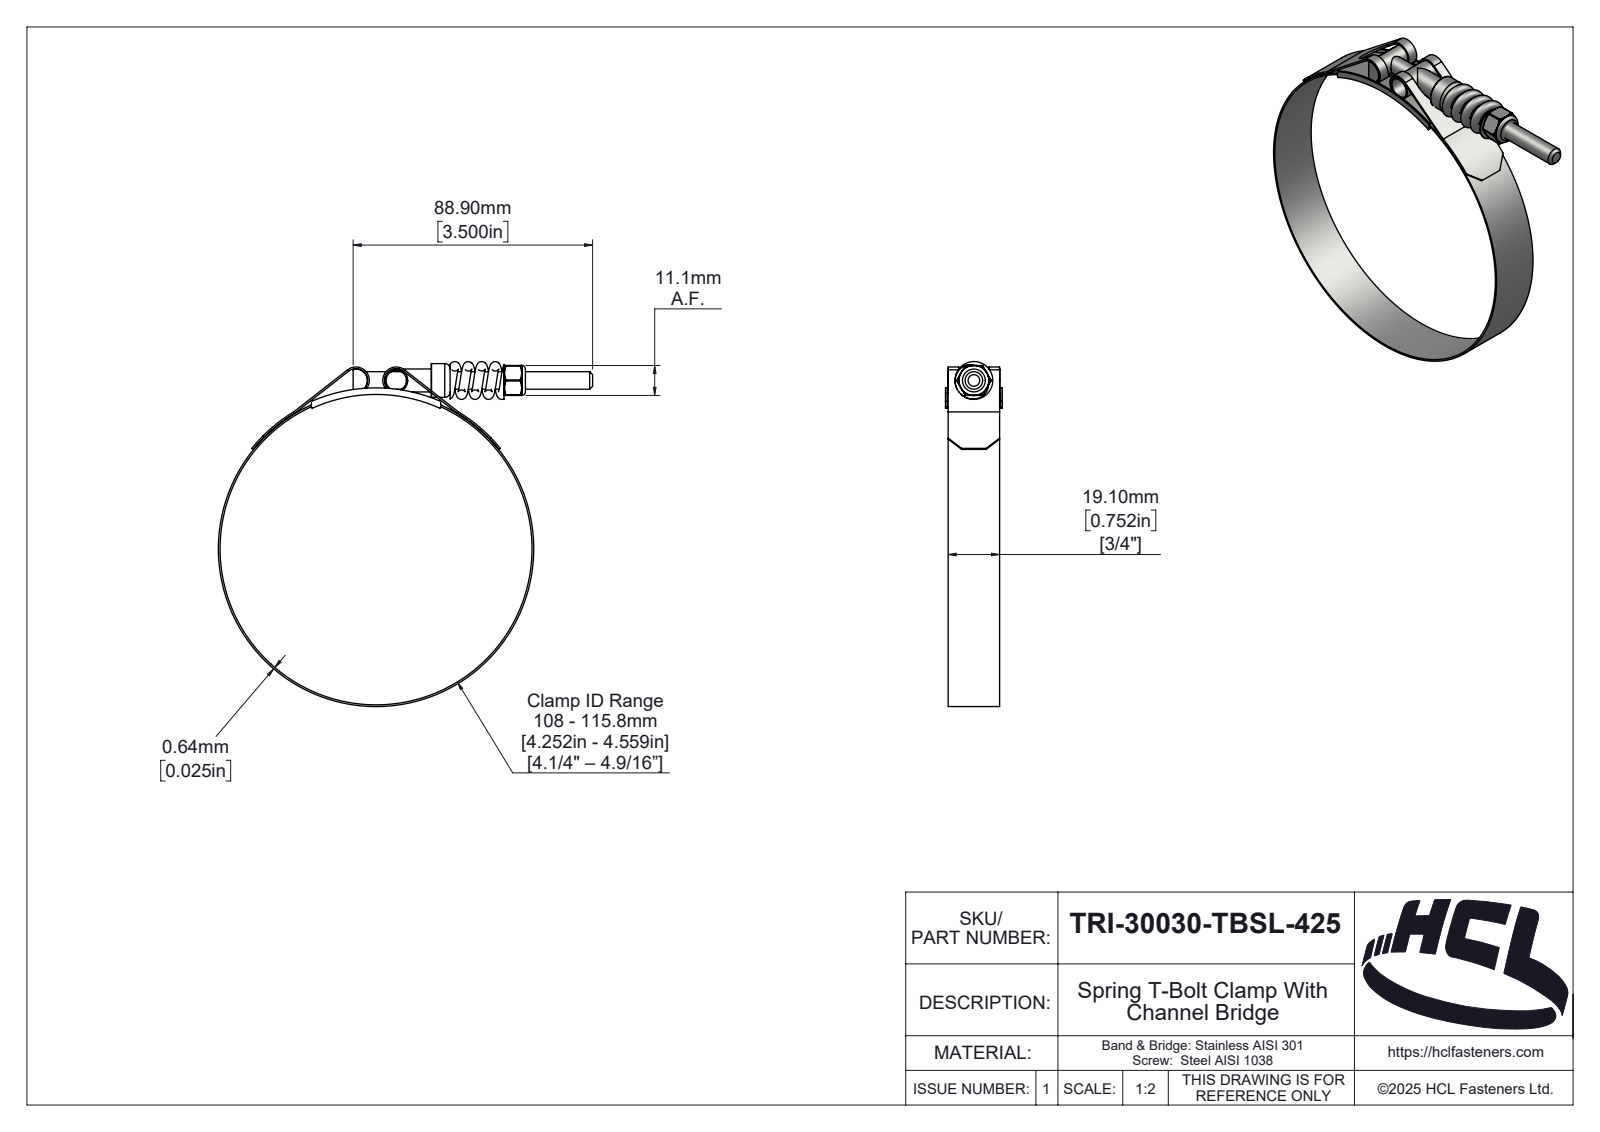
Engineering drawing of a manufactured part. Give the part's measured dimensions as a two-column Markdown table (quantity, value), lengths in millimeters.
| quantity | value |
| --- | --- |
| part name | TRI-30030-TBSL-425 |
| STEP written by | SolidWorks 2025 (AUTOMOTIVE_DESIGN) |
| units | millimeters |
| bodies | 7 solids, 332 faces (48 planar, 122 cylindrical, 162 other) |
| overall size | 139.94 × 128.01 × 21.1 |
| volume | 12 676 mm³ |
| surface area | 26 885 mm² |
| round holes (diameter × count) | 5.4 × 1, 6.35 × 1, 6.5 × 1, 7.52 × 1, 115.8 × 1 |
| round bosses / shafts (diameter × count) | 8.52 × 2, 117.08 × 1, 12.52 × 1 |
| partial cylindrical surfaces (radius × count) | 0.39 × 6, 0.5 × 2, 4.36 × 2, 5 × 2, 0.59 × 1, 2.42 × 1, 3.03 × 1, 3.19 × 1 |
| main face-to-face distances | 0.64, 19.1, 1, 20.1, 20.46, 0.36, 19.46, 21.1, 56, 11.11 |
| hole center spacings | 62.9 |
